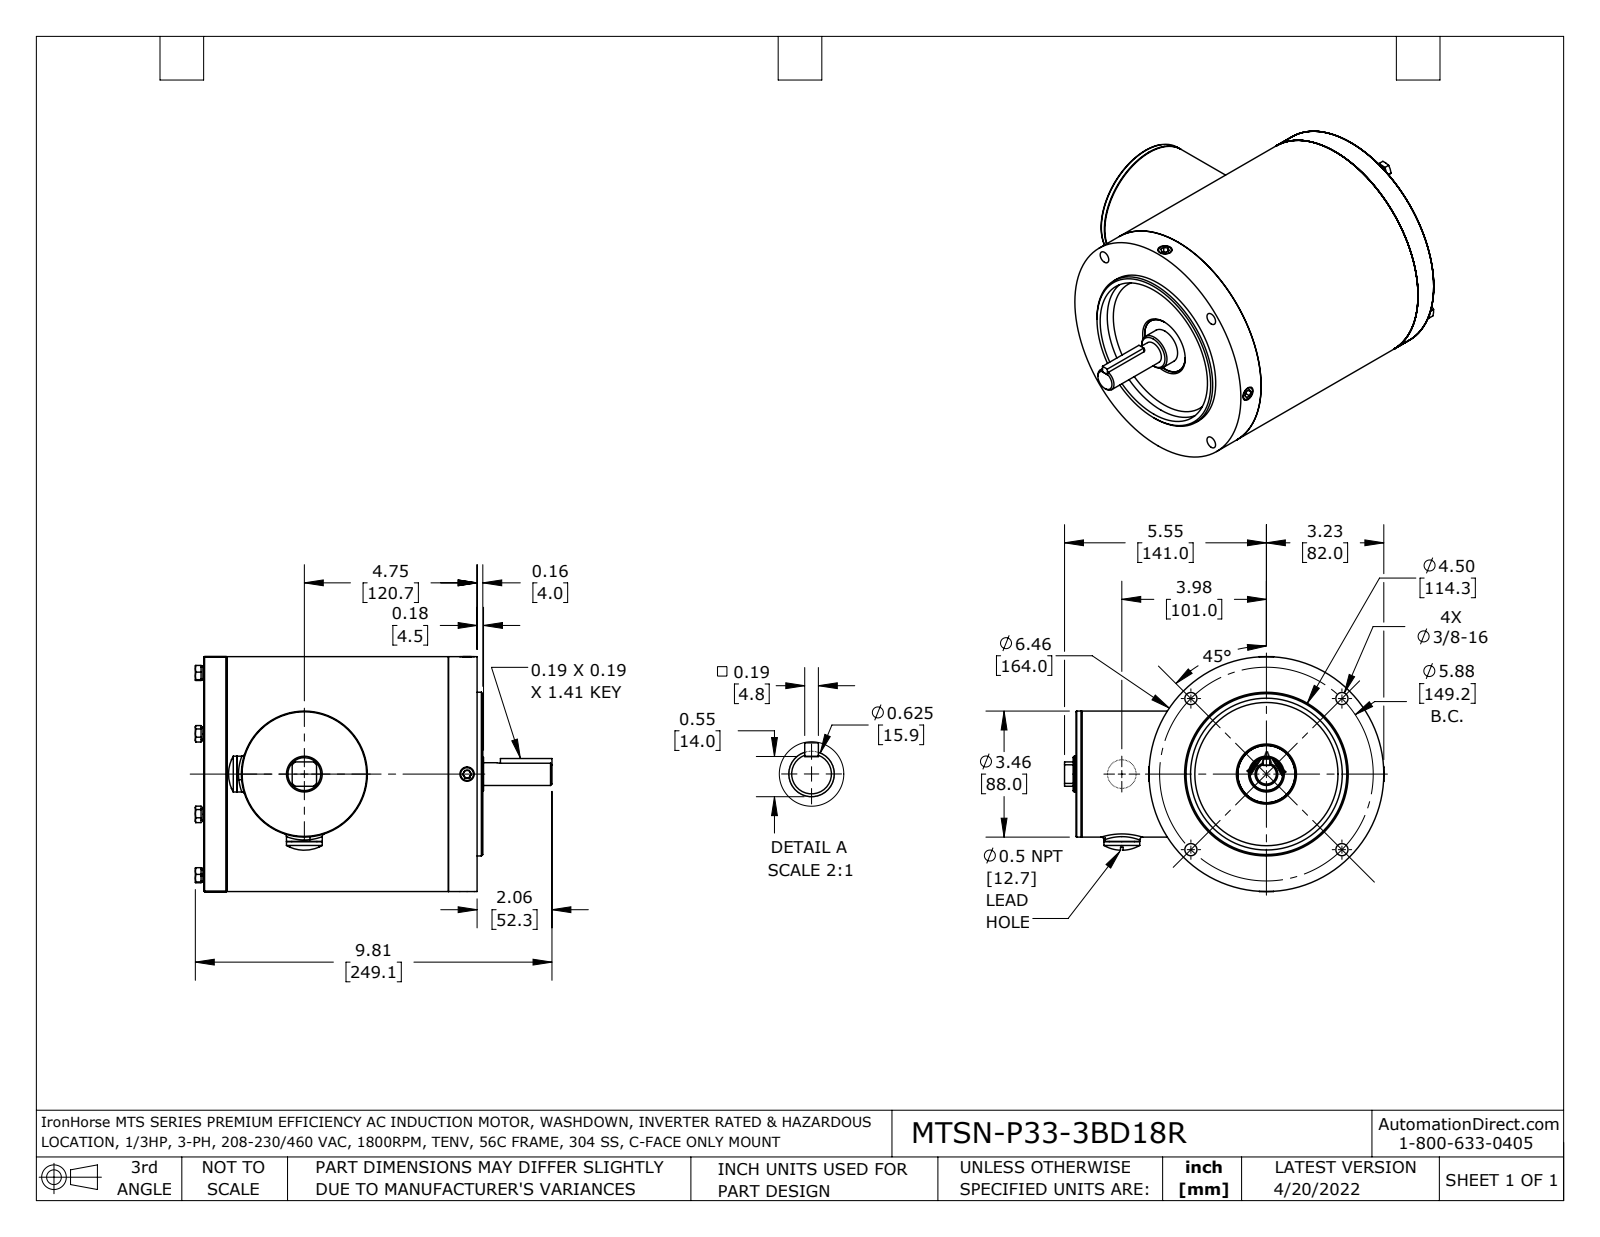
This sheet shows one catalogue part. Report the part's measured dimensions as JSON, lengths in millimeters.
{"part_name": "GG(MTSN-P33-3BD18R) nc WITH -bolts redcmb1 coord fxt", "step_written_by": "SolidWorks 2021 (AUTOMOTIVE_DESIGN)", "units": "millimeters", "bodies": {"solids": 6, "faces": 605, "planar": 221, "cylindrical": 217, "other": 167}, "overall_size": [249.1, 223, 164], "volume_mm3": 691700, "surface_area_mm2": 381800, "round_holes": [[4.2, 6], [8.5, 4], [3, 2], [16.7, 2], [35, 2], [26, 1], [42, 1], [52, 1], [66, 1], [78, 1], [82, 1], [106, 1]], "round_bosses_or_shafts": [[10, 6], [25, 4], [8, 4], [6, 4], [20, 2], [17.6, 2], [164, 1], [114.3, 1]], "partial_cylinders_radius": [[2, 16], [5.5, 4], [8, 4], [10, 4], [4.5, 2], [2.4, 1]], "face_to_face_distances": [3, 187.5, 6, 184.5, 181.5, 190.5, 9, 178.5, 4, 11], "hole_center_spacings": [74.6, 105.5, 30, 56.7, 63.4, 82.1, 87.9, 99.8]}
